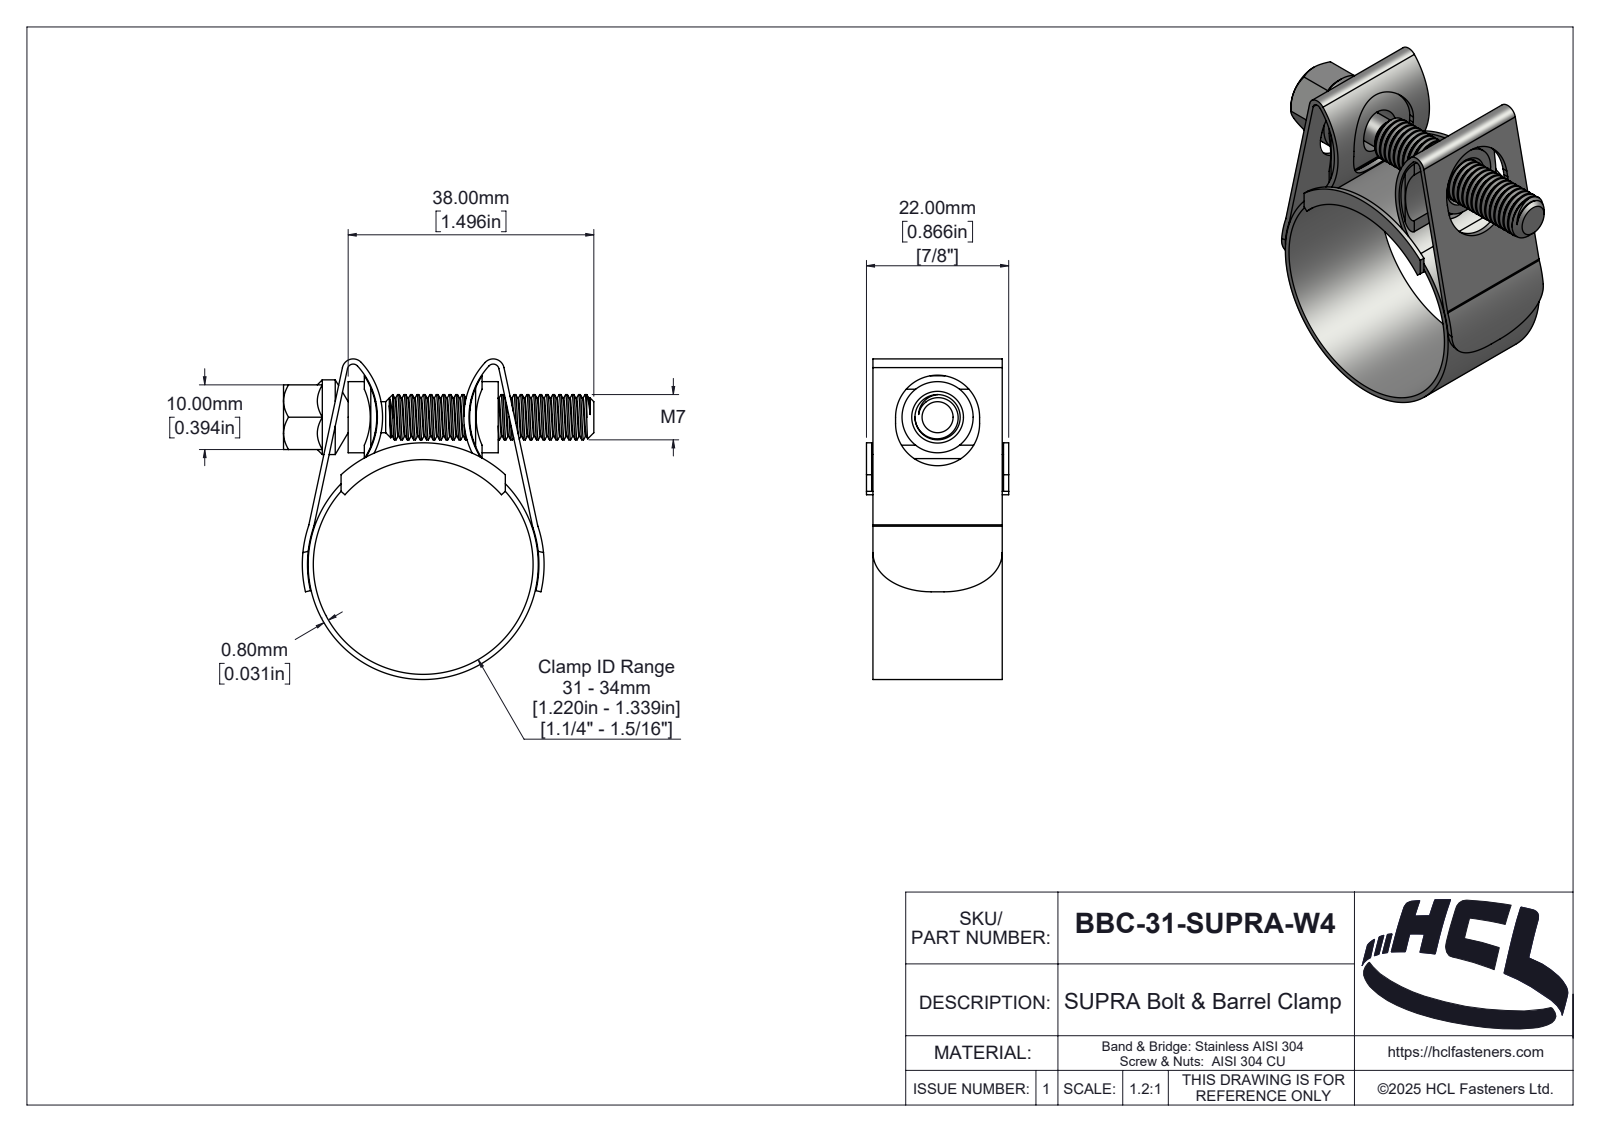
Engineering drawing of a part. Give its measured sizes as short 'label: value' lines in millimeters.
name: BBC-31-SUPRA-W4
written by: SolidWorks 2025 (AUTOMOTIVE_DESIGN)
unit: mm
bodies: 5 solids, 300 faces (46 planar, 174 cylindrical, 80 other)
size: 49.57 × 48 × 22
volume: 5 962 mm³; area: 11 651 mm²
holes: 1× ⌀34
bosses: 1× ⌀11.55, 1× ⌀11, 1× ⌀7, 1× ⌀4.8
rounds: 4× R1, 2× R0.9, 2× R1.7, 2× R2, 2× R2.8, 2× R6.5, 2× R10.62, 2× R11.62
face distances: 0.81, 20, 1, 21, 10, 0.8, 21.2, 20.2, 2.5, 20.72
